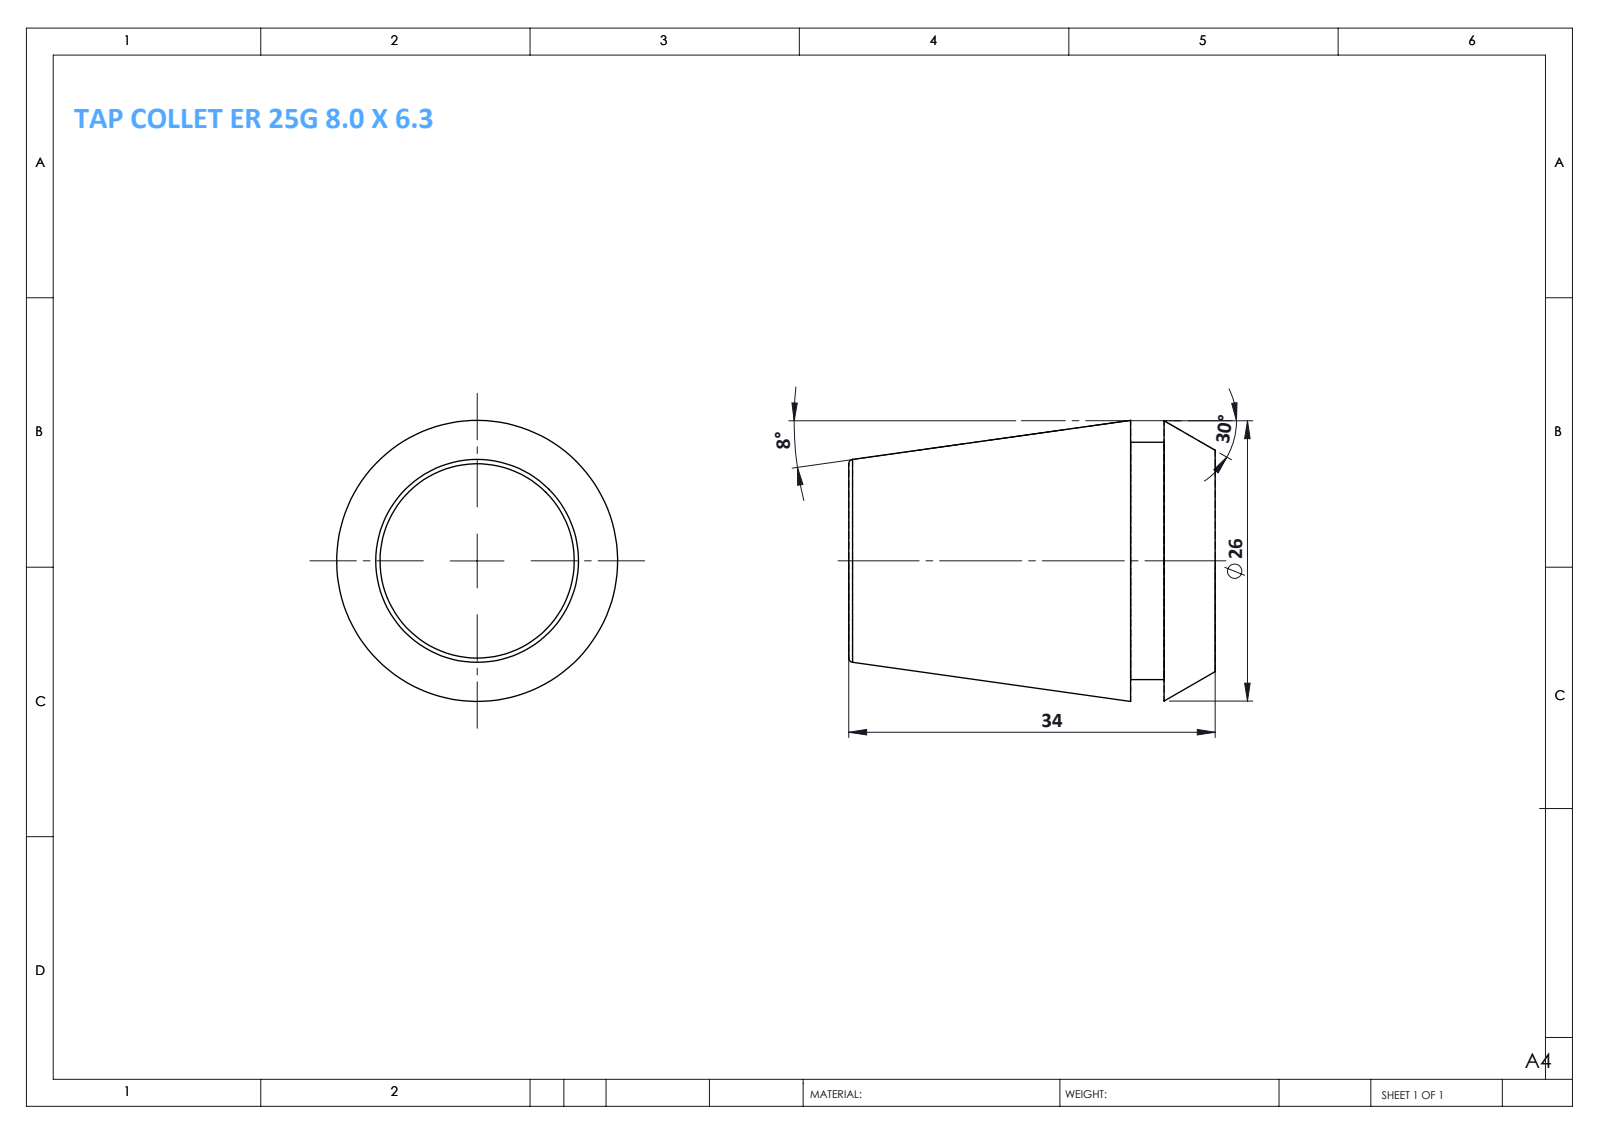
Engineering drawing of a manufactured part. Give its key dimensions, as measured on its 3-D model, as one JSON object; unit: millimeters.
{"part_name": "TAP COLLET ER 25G 8.0 X 6.3", "step_written_by": "SolidWorks 2014 (CONFIG_CONTROL_DESIGN)", "units": "millimeters", "bodies": {"solids": 1, "faces": 12, "planar": 4, "cylindrical": 2, "other": 6}, "overall_size": [34, 26.07, 26.07], "volume_mm3": 13600, "surface_area_mm2": 3376, "round_bosses_or_shafts": [[22, 1]], "face_to_face_distances": [34, 7.84, 26.16, 4.74, 3.1, 29.26]}
